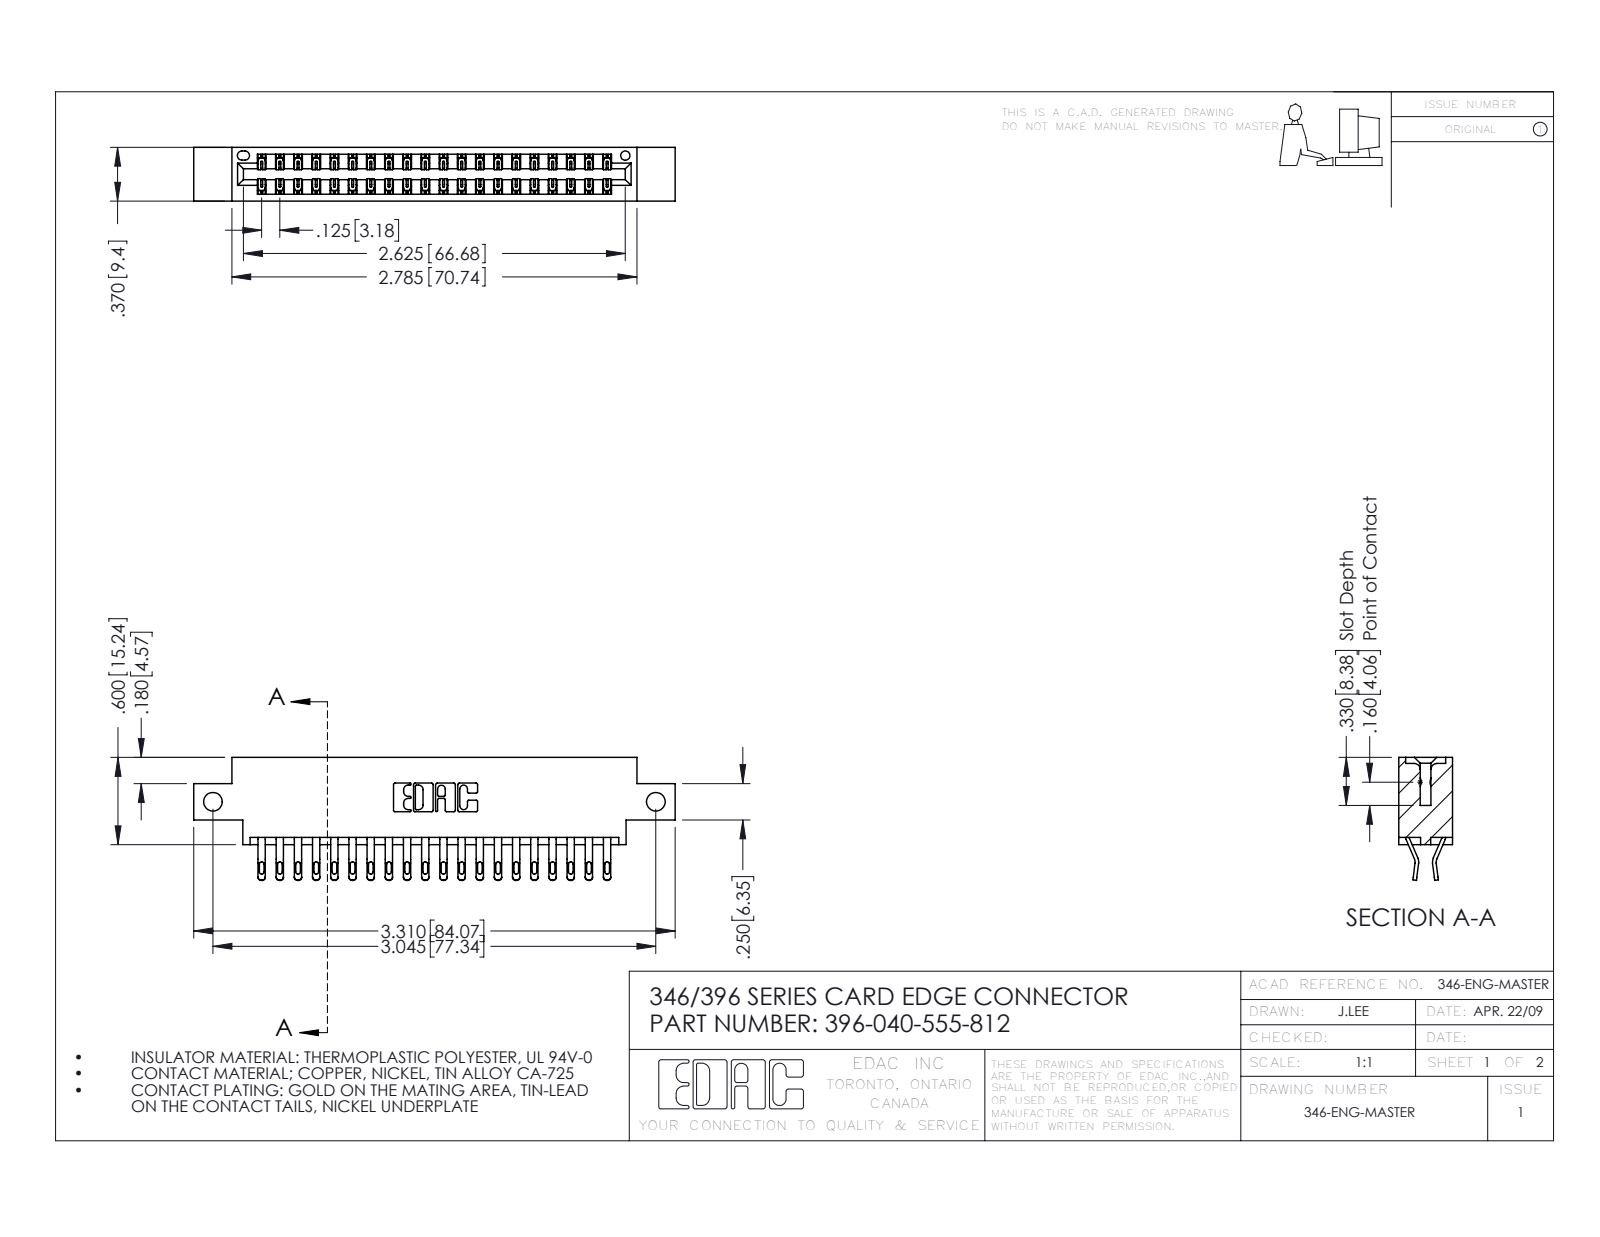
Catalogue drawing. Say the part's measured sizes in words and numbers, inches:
The part is named "345-292-001_555 Tail; 346 Part_0.170 Offset - Side Mount; 396-040-555-812". Its 3-D file was written by "SolidWorks 2016 (CONFIG_CONTROL_DESIGN)". It is 41 solids with 2446 faces: 1400 planar, 1046 cylindrical and 0 other. Overall it measures 3.31 by 0.845 by 0.37 inches. Its volume is 0.482 cubic inches and its surface area 17.01 square inches. Round holes: 2 of diameter 0.128, 1 of diameter 0.064. Partial cylindrical surfaces (rounded edges, fillets, slot ends): 80 of radius 0.016, 80 of radius 0.02, 60 of radius 0.006, 22 of radius 0.01, 6 of radius 0.007, 6 of radius 0.031, 3 of radius 0.026, 2 of radius 0.01. The main face-to-face distances are 0.048, 0.322, 0.37, 0.25, 0.025, 0.072, 0.298, 0.275, 0.148, 0.222. The hole center spacings are 3.045.
